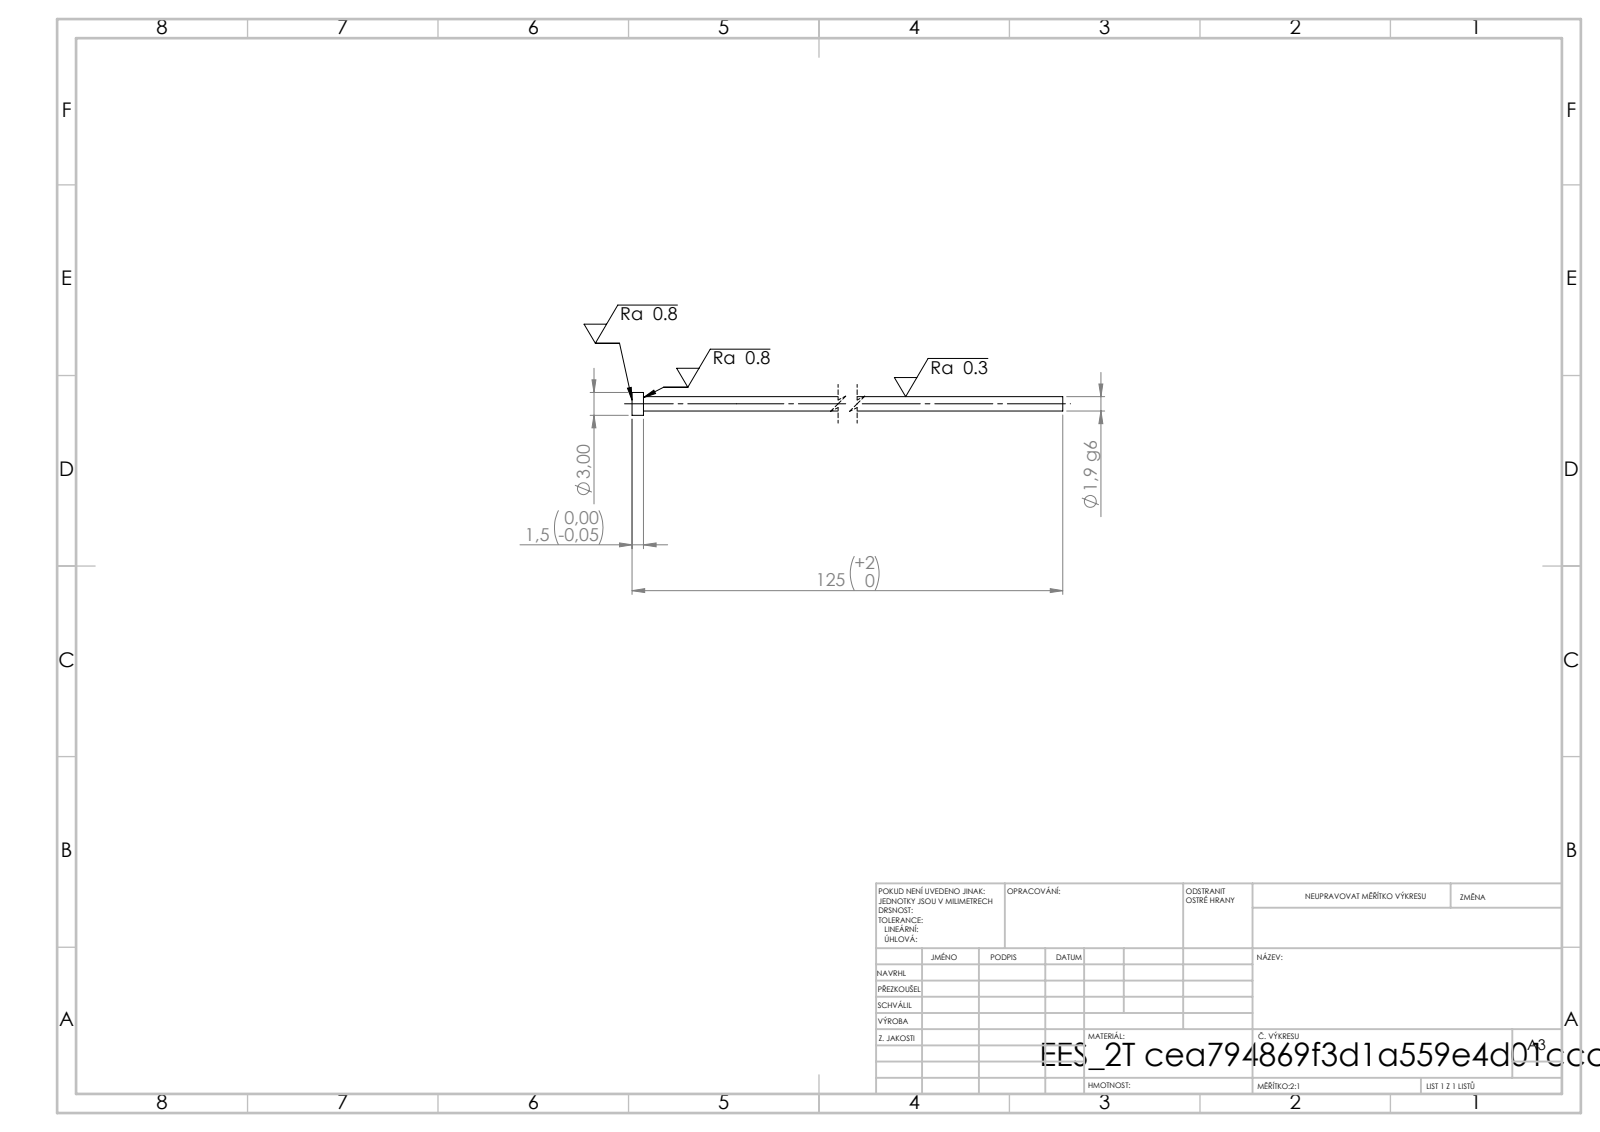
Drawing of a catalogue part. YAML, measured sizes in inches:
step_written_by: "SolidWorks 2019 (CONFIG_CONTROL_DESIGN)"
units: inches
bodies: {solids: 1, faces: 7, planar: 3, cylindrical: 4, other: 0}
overall_size: [4.921, 0.118, 0.118]
volume: 0.022
surface_area: 1.19
round_bosses_or_shafts:
  - {diameter: 0.118, count: 1}
  - {diameter: 0.075, count: 1}
face_to_face_distances: [0.059, 4.921, 4.862]
